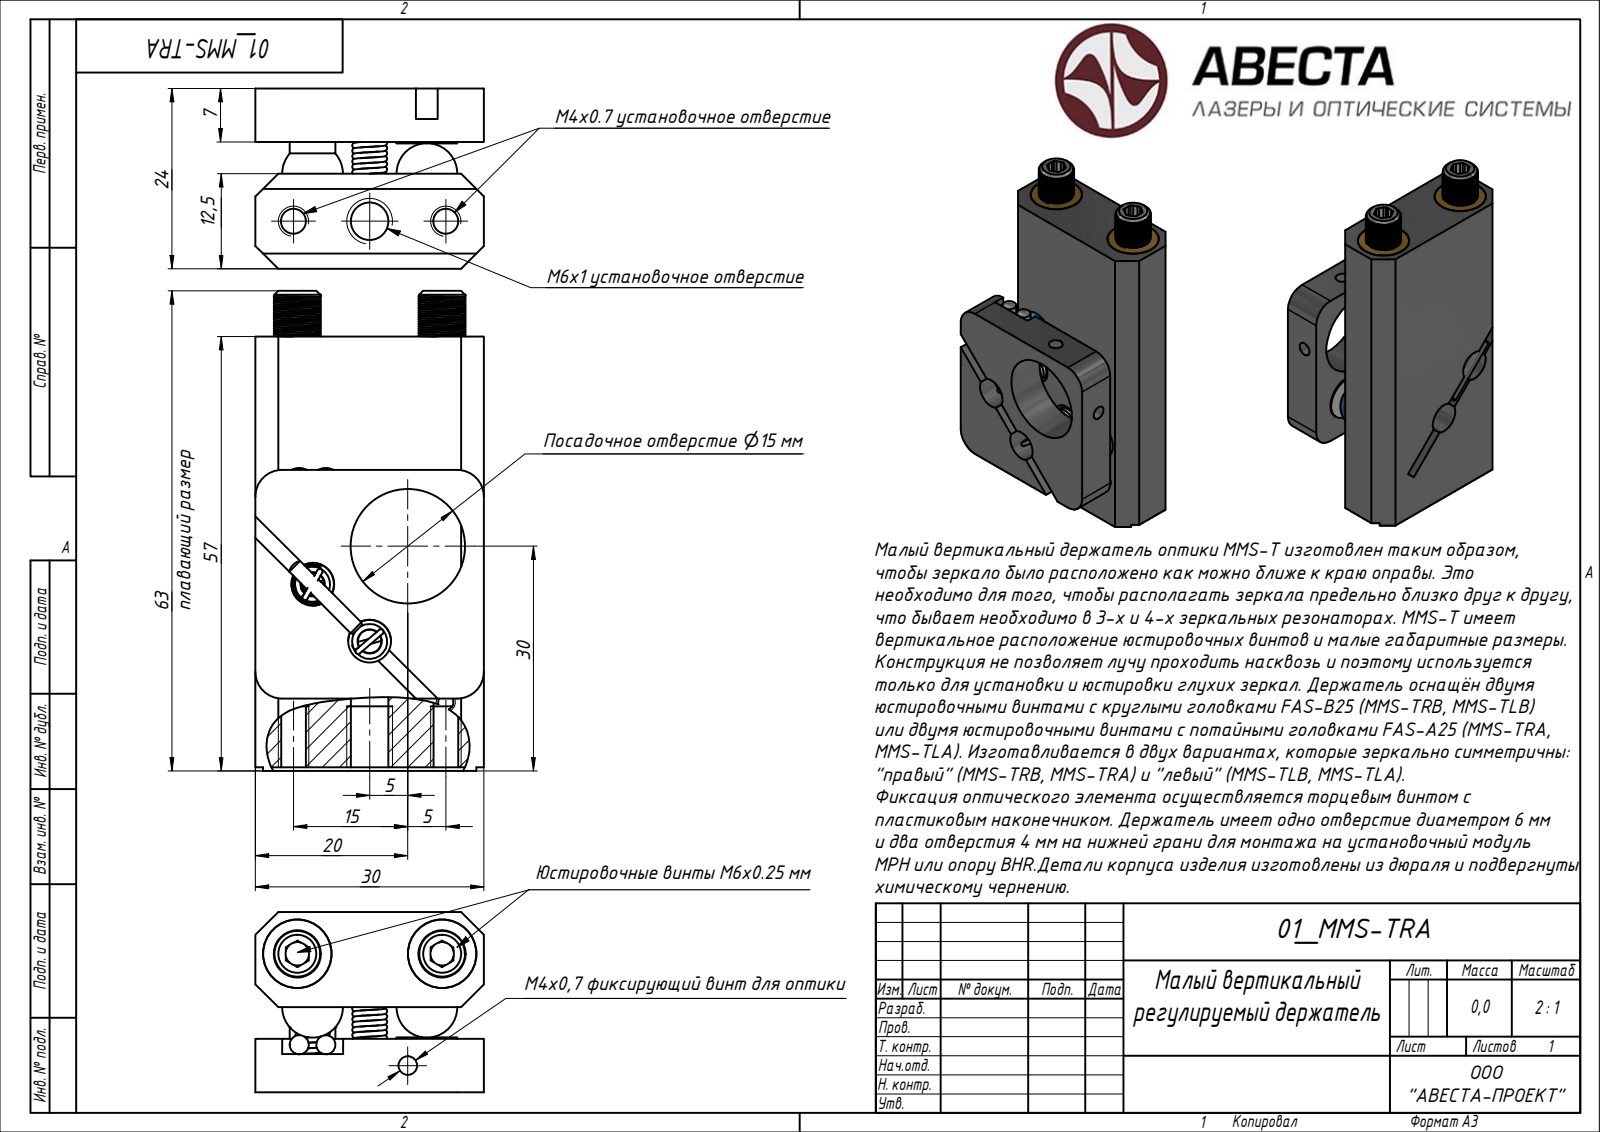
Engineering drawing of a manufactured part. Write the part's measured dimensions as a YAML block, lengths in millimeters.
step_written_by: "ST-DEVELOPER v15 (AUTOMOTIVE_DESIGN)"
units: millimeters
bodies: {solids: 15, faces: 260, planar: 106, cylindrical: 0, other: 154}
overall_size: [61, 30, 23.66]
volume: 23144
surface_area: 15654
face_to_face_distances: [12.5, 30, 11.16, 23.66, 16.66, 25.8, 7, 4.16, 2, 56.5]
